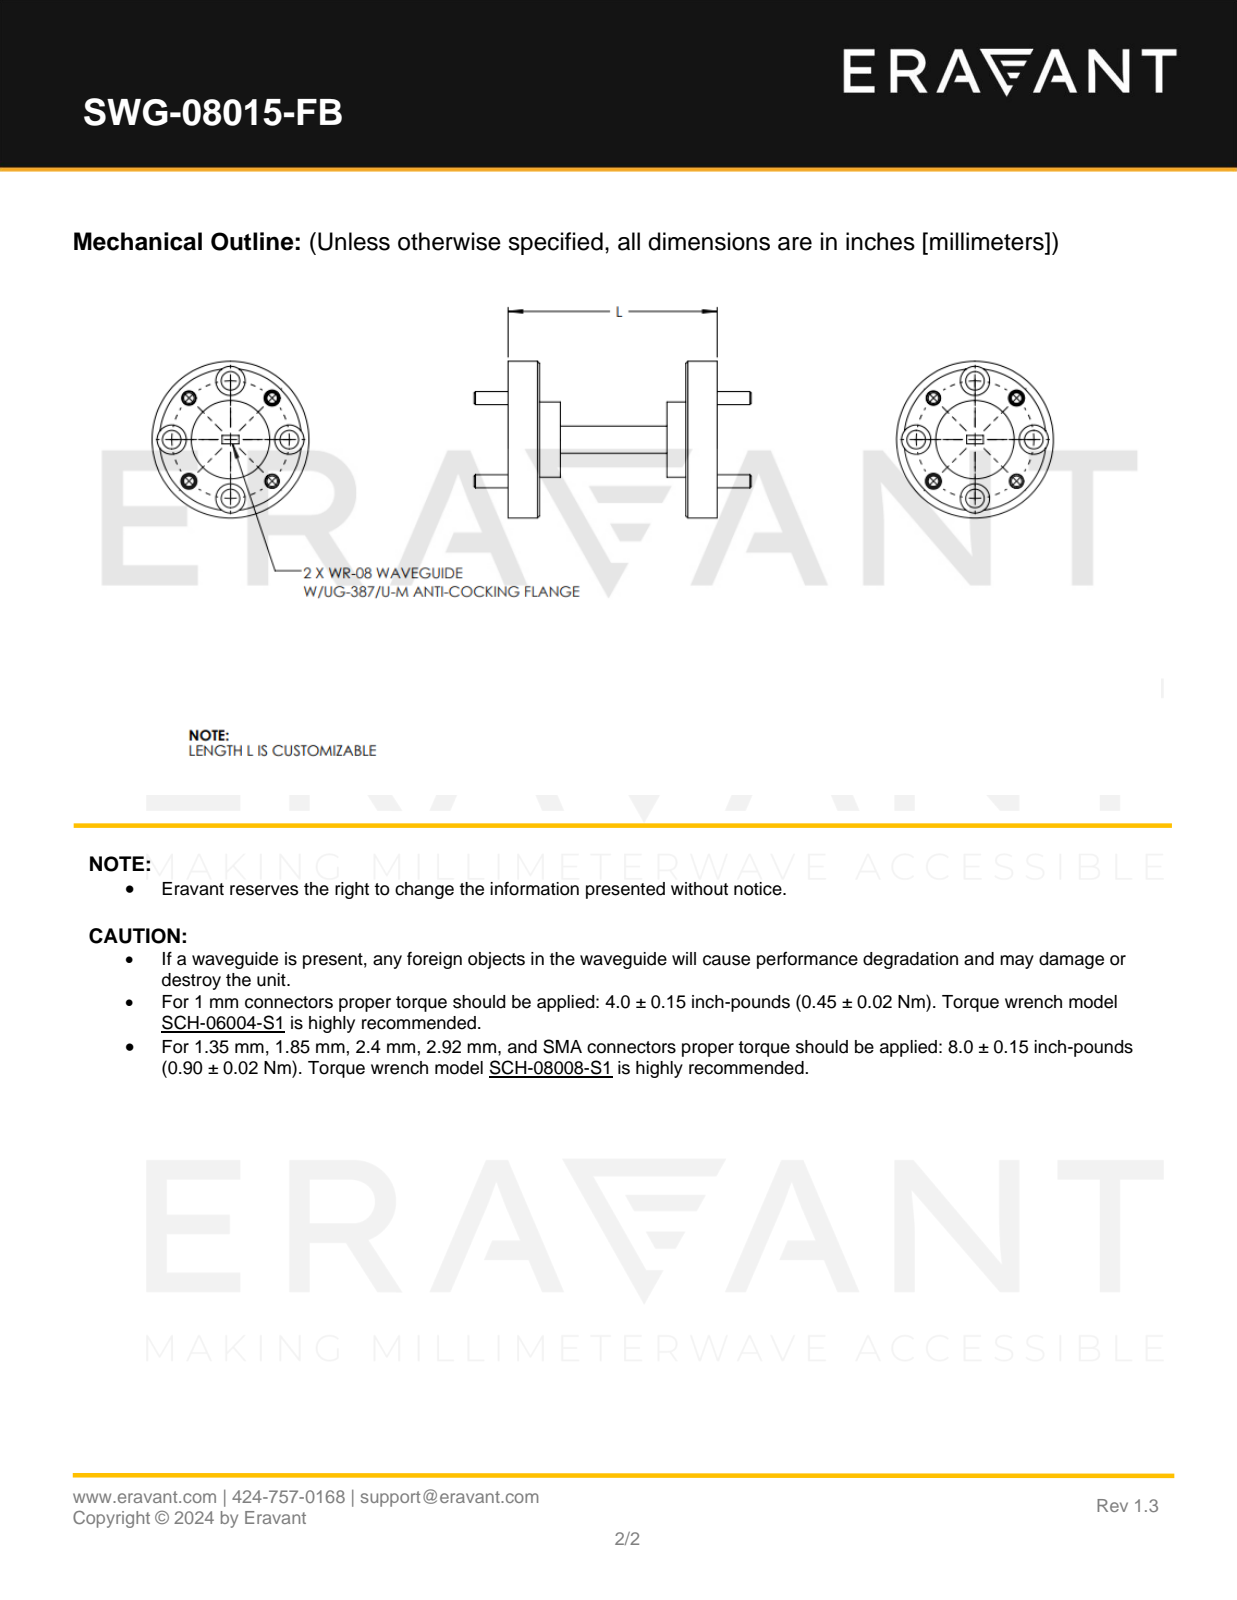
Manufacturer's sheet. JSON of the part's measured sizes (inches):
{"part_name": "SWG-08015-FB", "step_written_by": "SolidWorks 2021 (CONFIG_CONTROL_DESIGN)", "units": "inches", "bodies": {"solids": 5, "faces": 146, "planar": 38, "cylindrical": 68, "other": 40}, "overall_size": [1.805, 0.75, 0.75], "volume_in3": 0.155, "surface_area_in2": 3.809, "round_holes": [[0.06, 4], [0.067, 4], [0.089, 4], [0.14, 4]], "round_bosses_or_shafts": [[0.063, 4], [0.75, 1], [0.375, 1], [0.36, 1]], "face_to_face_distances": [0.13, 1.31, 1.18, 1.44, 0.03, 0.16, 1.34, 1.47, 0.13, 0.25], "hole_center_spacings": [0.215, 0.398, 0.52, 0.563, 0.398, 0.519, 0.562]}
